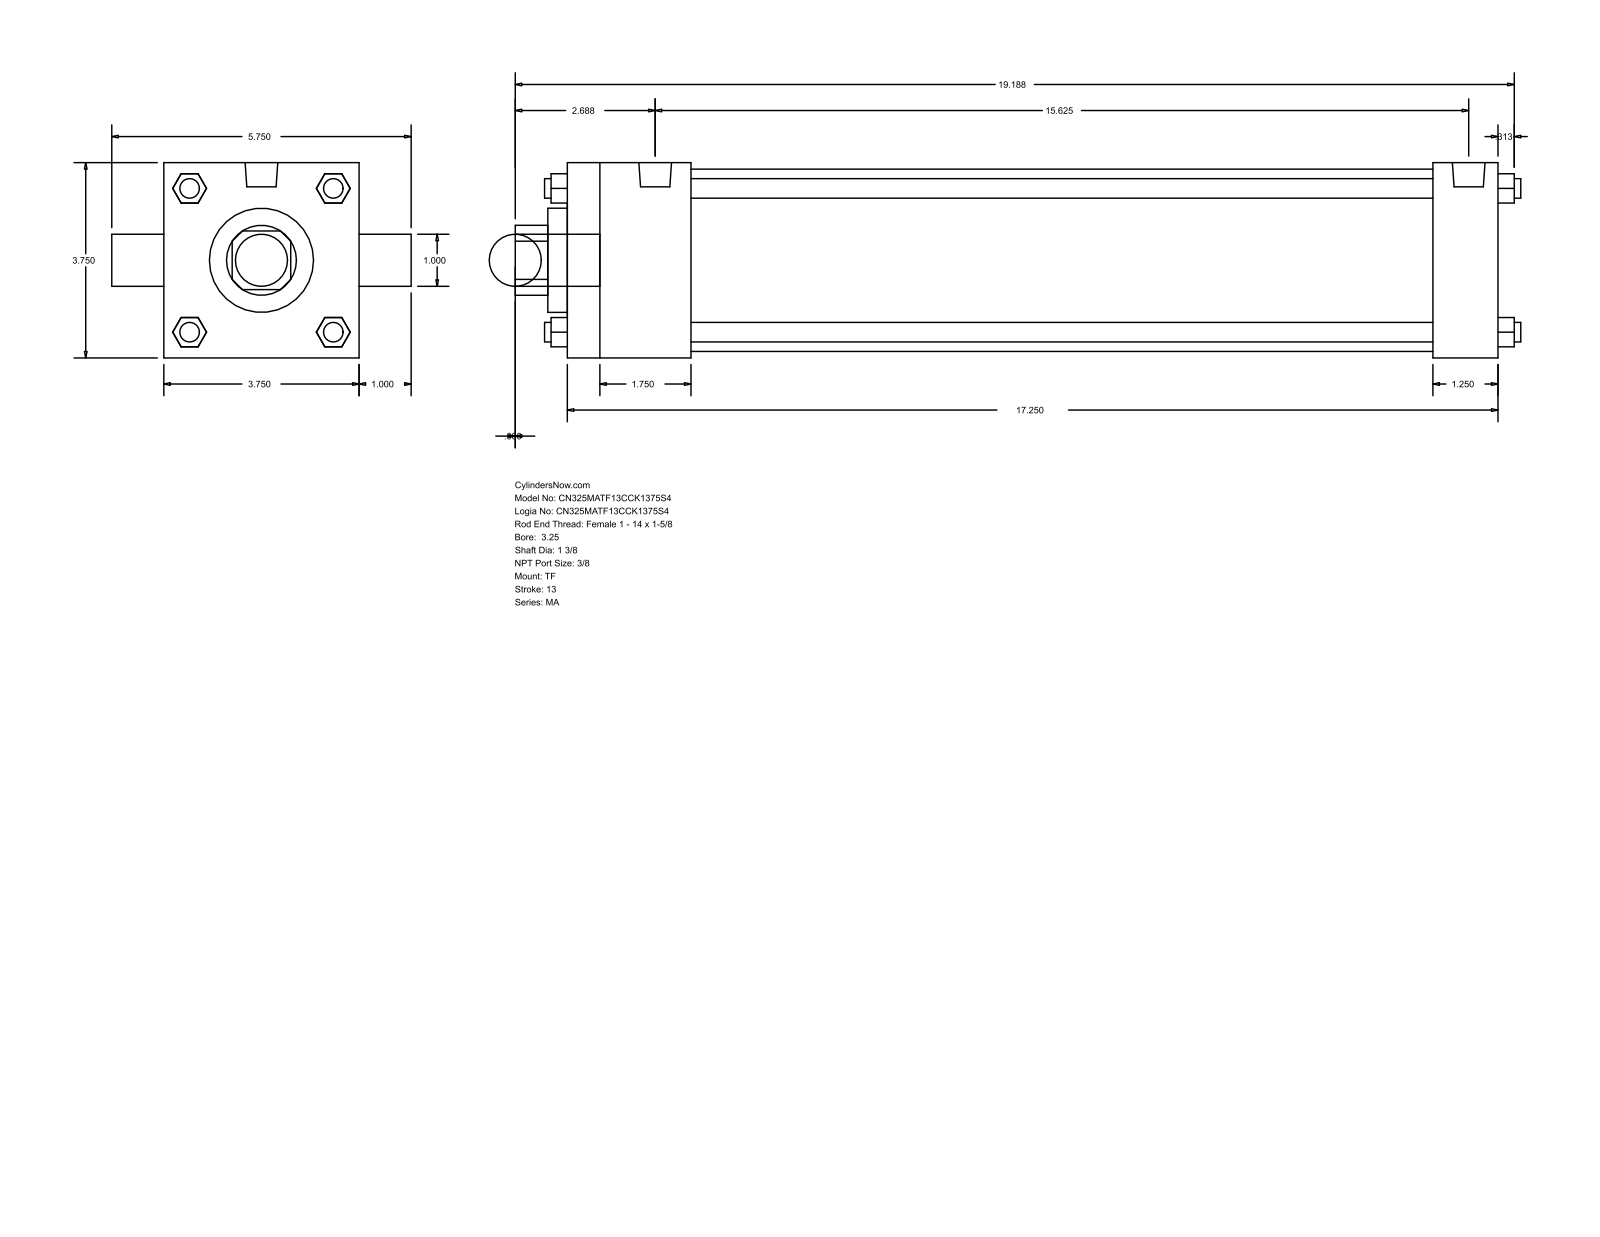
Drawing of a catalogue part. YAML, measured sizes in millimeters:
part_name: "MA_TF__0325_1.375"
step_written_by: "GSSL Pune (CONFIG_CONTROL_DESIGN)"
units: millimeters
bodies: {solids: 0, faces: 120, planar: 92, cylindrical: 28, other: 0}
overall_size: [490.54, 146.05, 95.25]
round_holes:
  - {diameter: 25.4, count: 1}
  - {diameter: 34.92, count: 1}
  - {diameter: 50.8, count: 1}
  - {diameter: 88.9, count: 1}
round_bosses_or_shafts:
  - {diameter: 9.53, count: 4}
  - {diameter: 11.11, count: 3}
  - {diameter: 15.93, count: 2}
  - {diameter: 25.4, count: 1}
partial_cylinders:
  - {radius: 17.06, count: 1}
face_to_face_distances: [95.24, 454.03, 60.32, 422.28, 361.96, 393.71, 31.75, 9.52, 69.84, 431.8]
